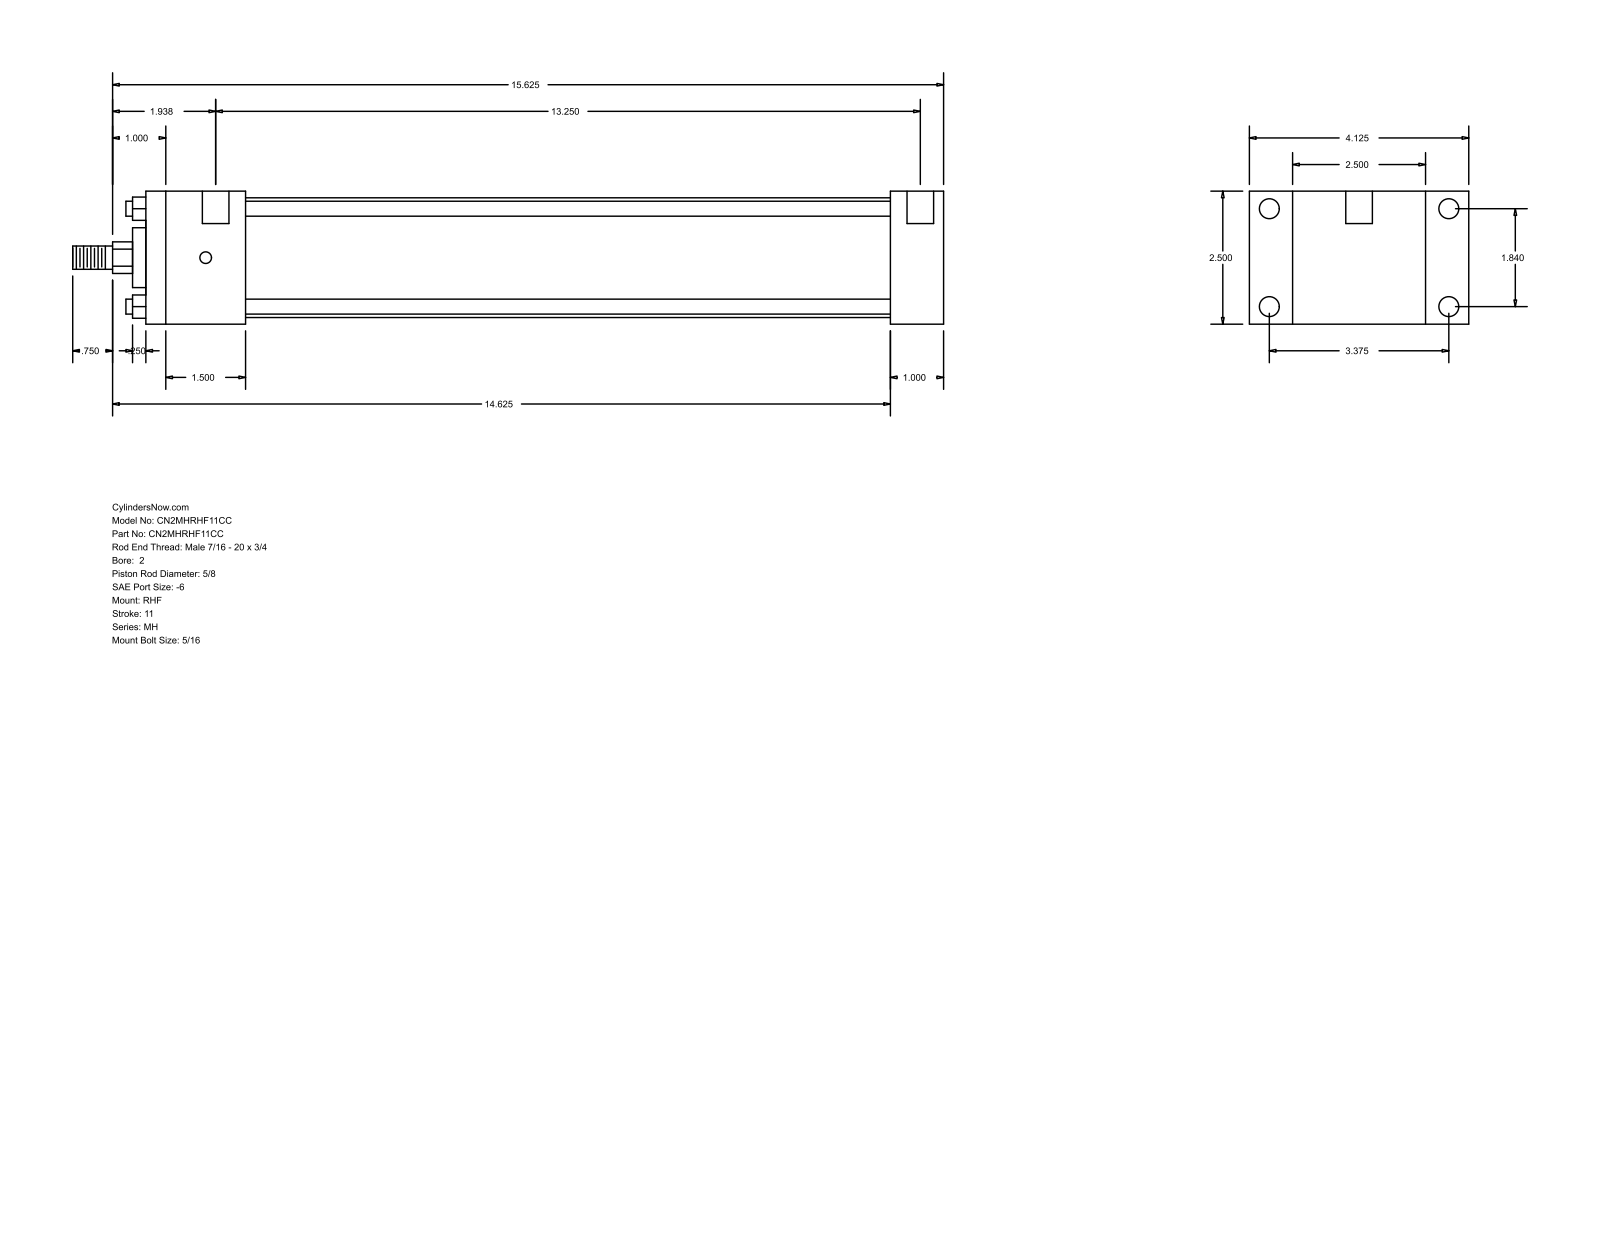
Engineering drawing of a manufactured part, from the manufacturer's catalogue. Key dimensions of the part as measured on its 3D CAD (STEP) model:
Part name (STEP PRODUCT): MH_RHF__0200_0.625
STEP written by: GSSL Pune (CONFIG_CONTROL_DESIGN)
Units: millimetres
Bodies: 0 solids, 88 faces (60 planar, 28 cylindrical, 0 other)
Overall size (bounding box): 415.93 × 104.78 × 63.5
Round holes (diameter × count): ⌀5.56 ×4, ⌀9.53 ×4, ⌀12.7 ×2
Round bosses / shafts (diameter × count): ⌀7.14 ×4, ⌀57.15 ×1, ⌀28.57 ×1, ⌀15.88 ×1, ⌀11.11 ×1
Partial cylindrical surfaces — rounded edges, fillets, slot ends (radius × count): R7.54 ×1
Main face-to-face distances: 63.5, 25.4, 20.64, 84.14, 355.6, 381, 104.78, 47.62, 307.98, 333.38
Hole centre spacings: 46.74, 85.72, 97.63, 344.49, 3.18, 4.76, 336.55, 339.73
